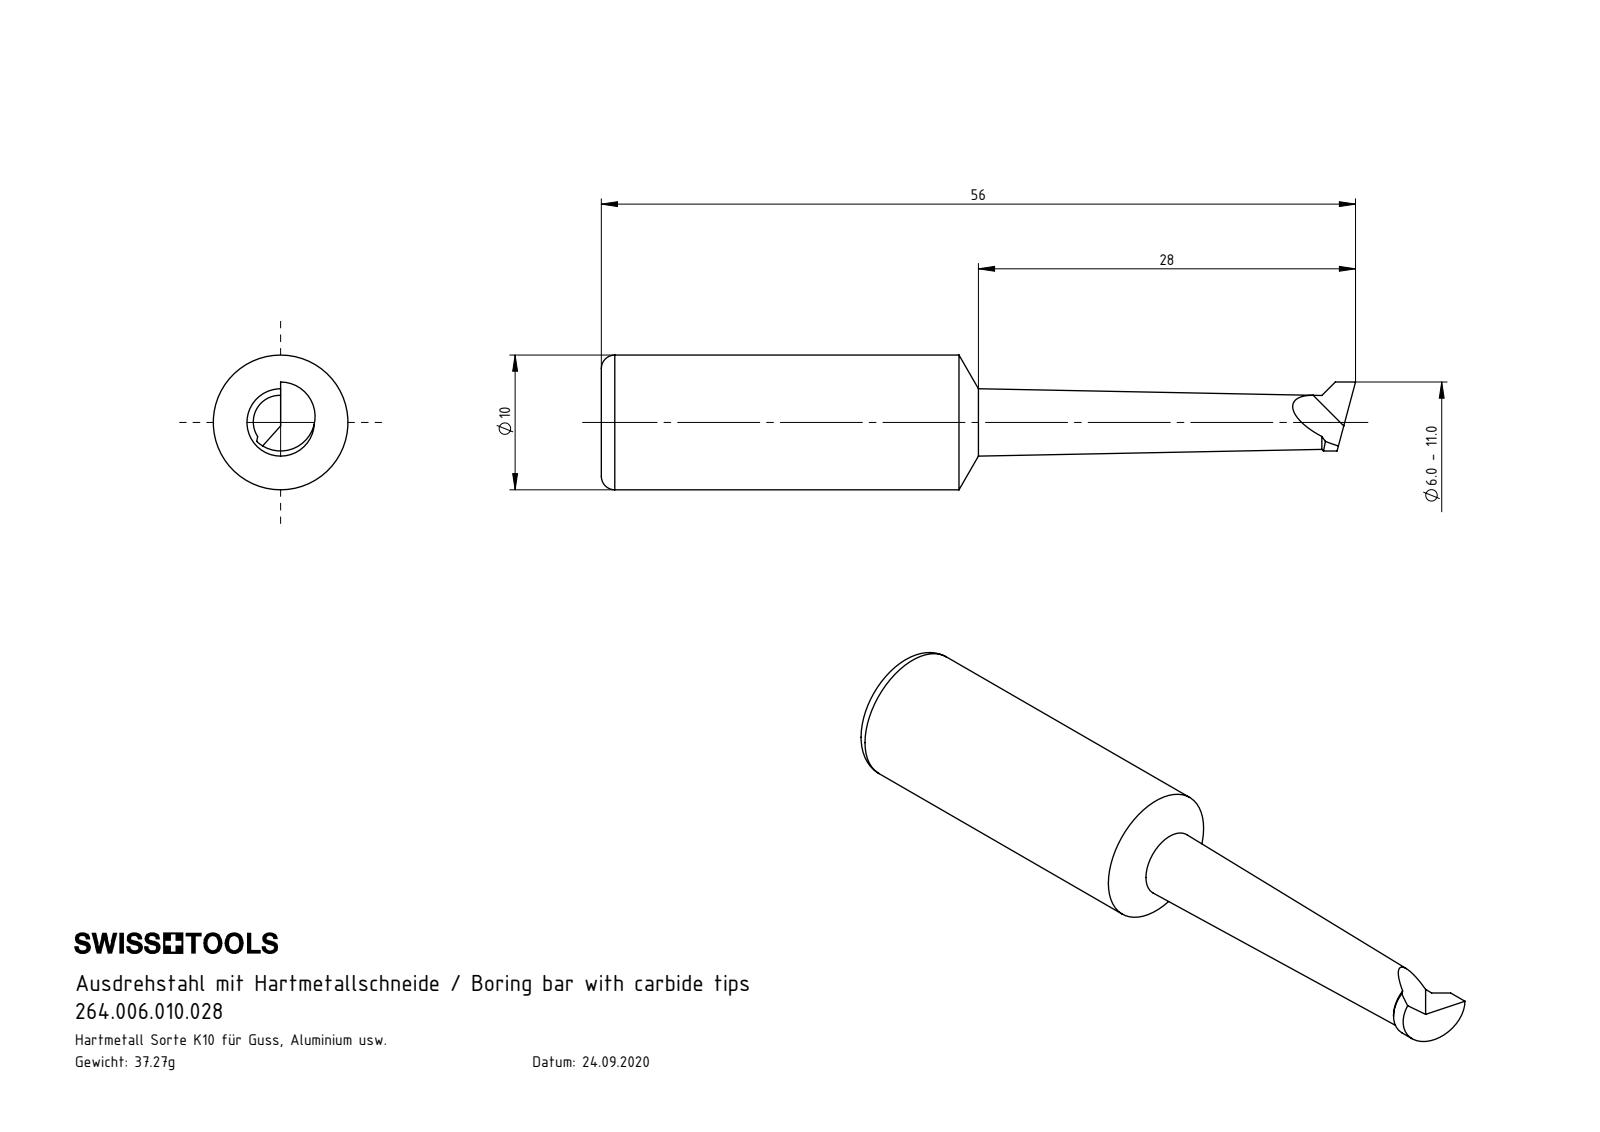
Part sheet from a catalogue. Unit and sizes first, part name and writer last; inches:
Units: inches
Overall size (bounding box): 2.205 × 0.394 × 0.394
Round bosses / shafts (diameter × count): ⌀0.394 ×1
Partial cylindrical surfaces — rounded edges, fillets, slot ends (radius × count): R0.101 ×1
Volume: 0.157 in³ · Surface area: 2.119 in²
Bodies: 1 solid, 10 faces (4 planar, 2 cylindrical, 4 other)
Part name (STEP PRODUCT): U10.B06.001.028
STEP written by: SolidWorks 2017 (AUTOMOTIVE_DESIGN)
